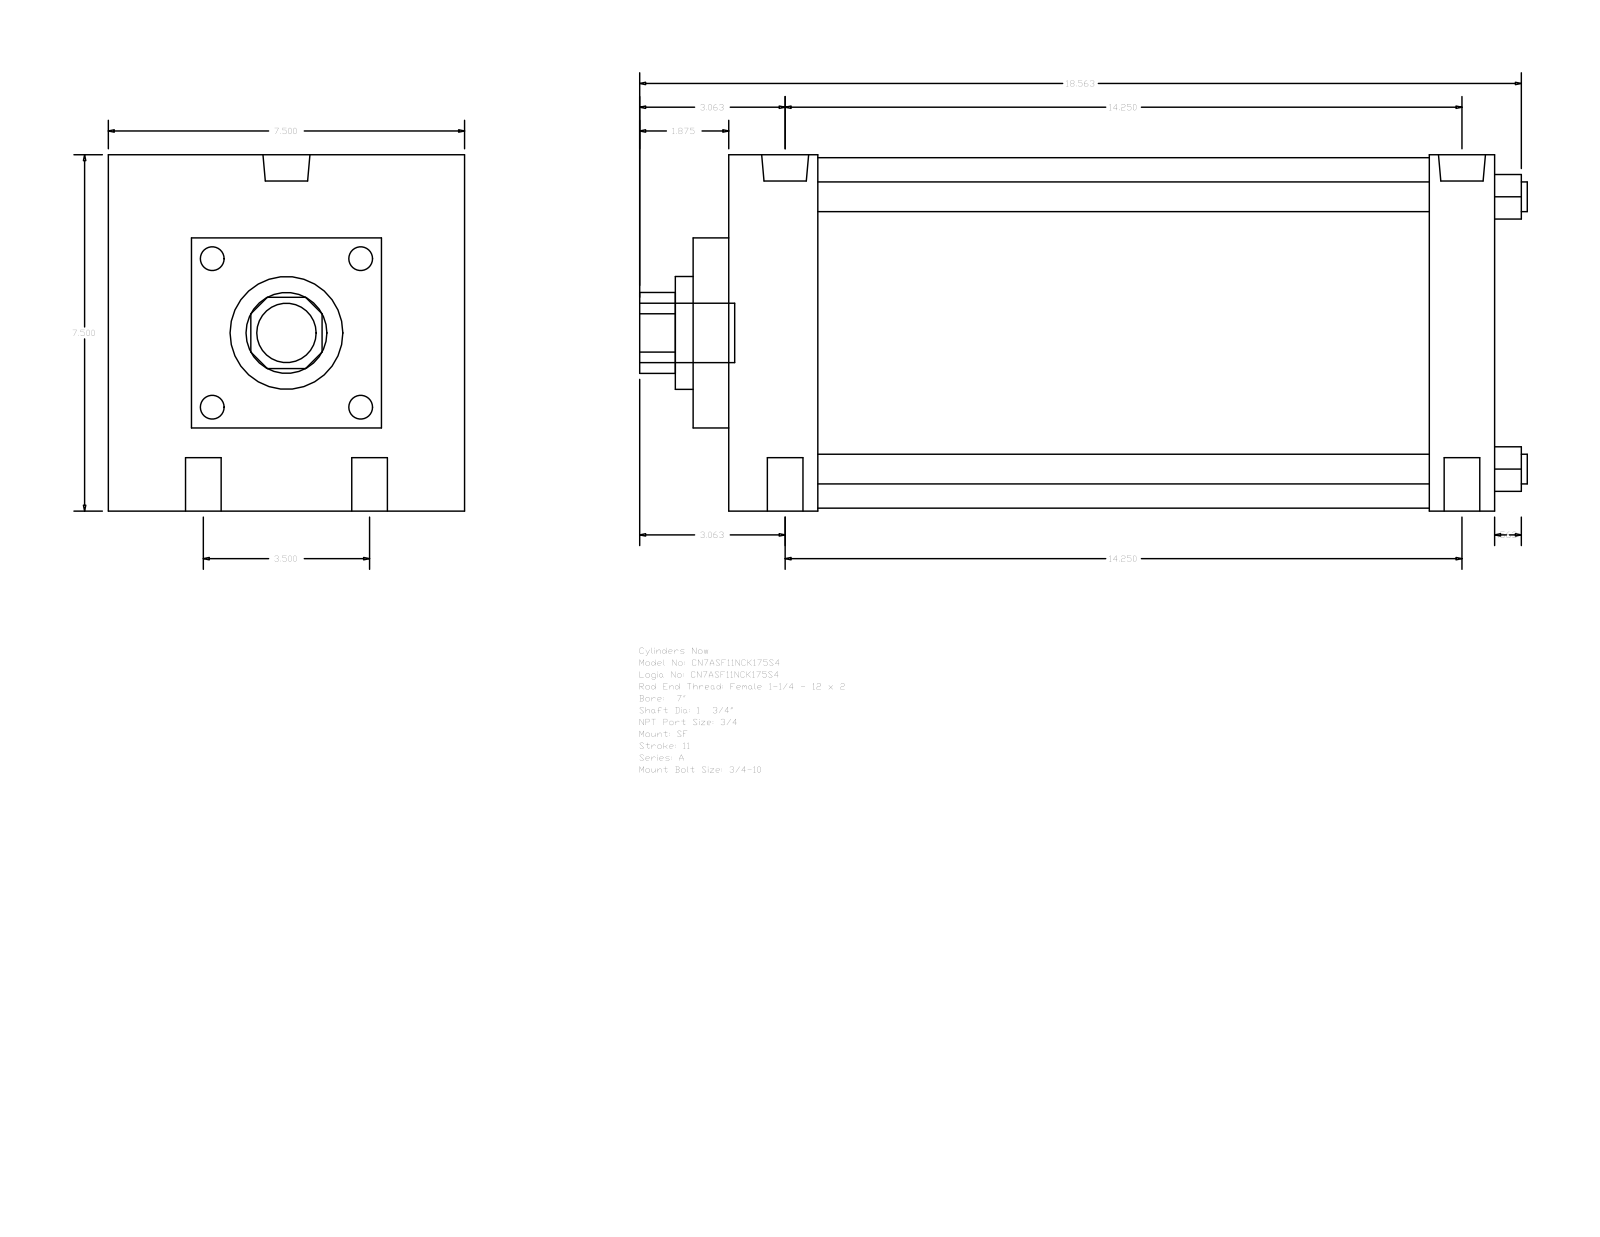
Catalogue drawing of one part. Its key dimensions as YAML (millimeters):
part_name: "A_SF__0700_1.75"
step_written_by: "GSSL Pune (CONFIG_CONTROL_DESIGN)"
units: millimeters
bodies: {solids: 0, faces: 93, planar: 67, cylindrical: 26, other: 0}
overall_size: [474.66, 190.5, 190.5]
round_holes:
  - {diameter: 19.05, count: 4}
  - {diameter: 15.08, count: 2}
  - {diameter: 25.12, count: 2}
  - {diameter: 44.45, count: 1}
  - {diameter: 60.33, count: 1}
round_bosses_or_shafts:
  - {diameter: 15.88, count: 4}
  - {diameter: 187.32, count: 1}
  - {diameter: 31.75, count: 1}
partial_cylinders:
  - {radius: 21.63, count: 1}
face_to_face_distances: [190.5, 409.58, 44.45, 19.05, 47.63, 374.65, 327.02, 361.95, 34.93, 146.05]
hole_center_spacings: [44.45, 364.67, 361.95, 88.9, 372.71, 350.83]
